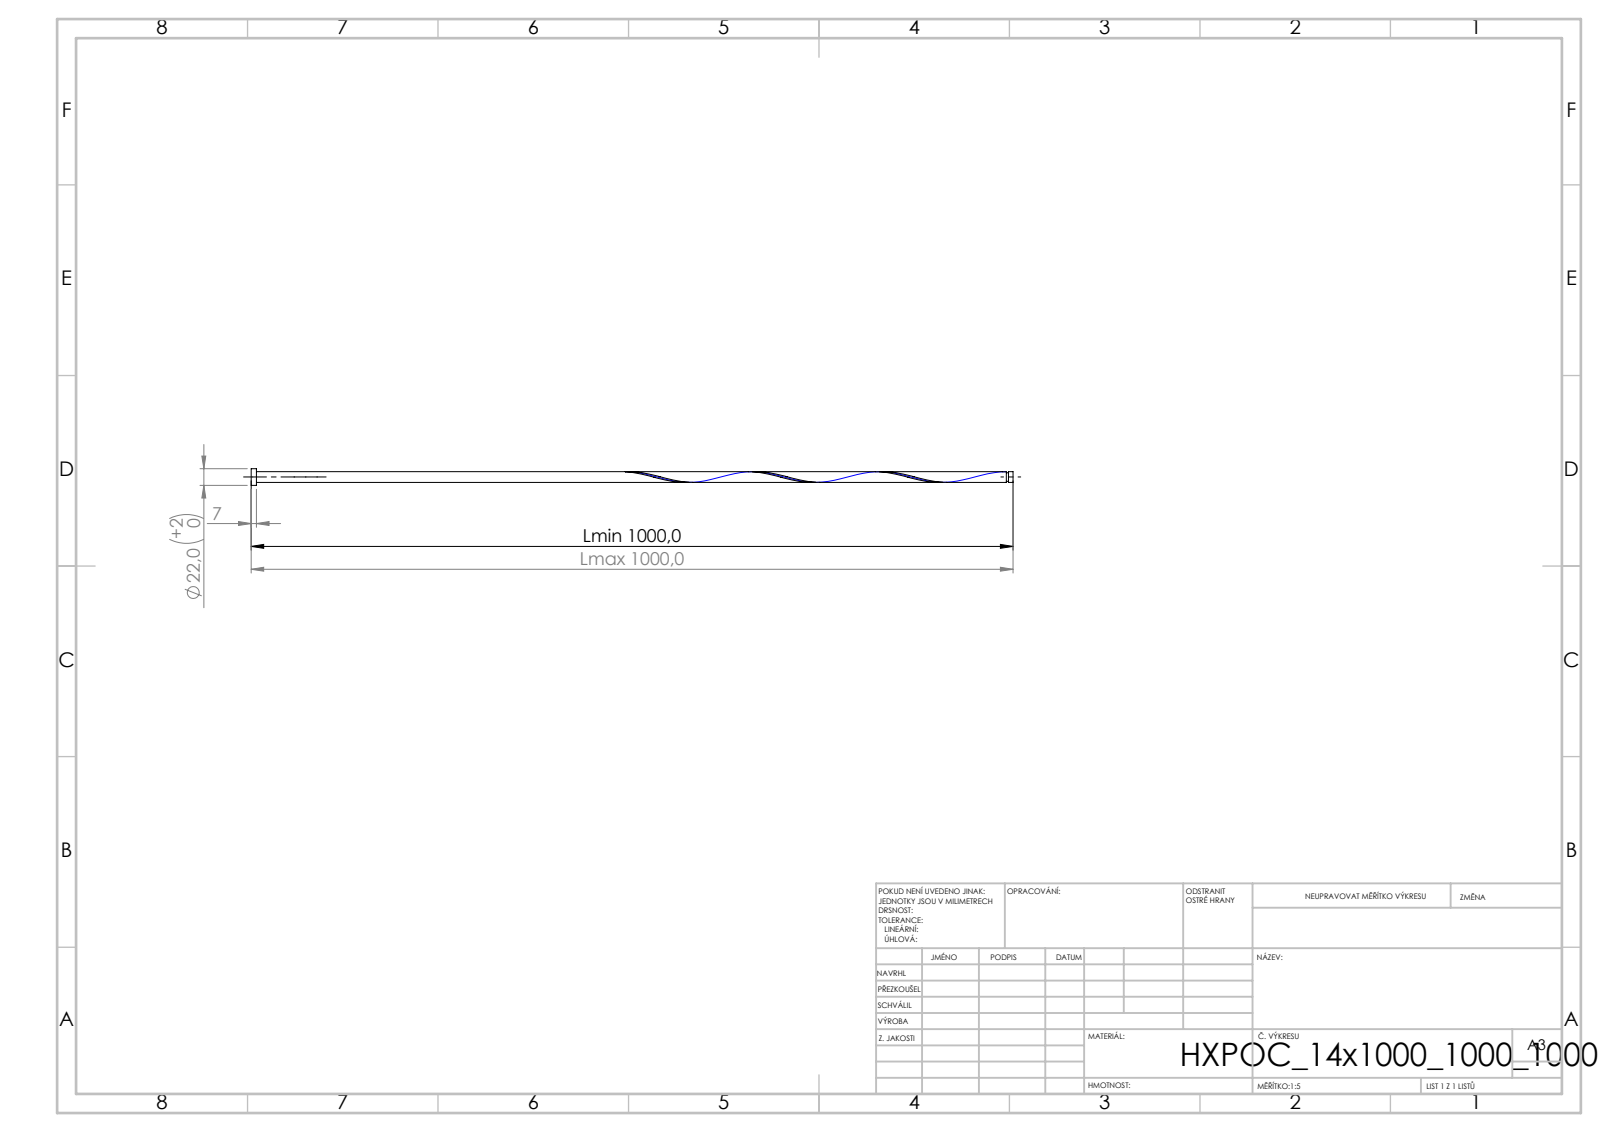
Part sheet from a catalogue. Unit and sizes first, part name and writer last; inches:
Units: inches
Overall size (bounding box): 39.37 × 0.866 × 0.866
Round bosses / shafts (diameter × count): ⌀0.866 ×1, ⌀0.551 ×1, ⌀0.441 ×1
Main face-to-face distances: 0.276, 39.37, 39.094, 39.131, 38.856, 0.239, 39.021, 38.746, 0.11, 0.349
Volume: 11.48 in³ · Surface area: 93.55 in²
Bodies: 1 solid, 16 faces (6 planar, 9 cylindrical, 1 other)
STEP written by: SolidWorks 2019 (CONFIG_CONTROL_DESIGN)
